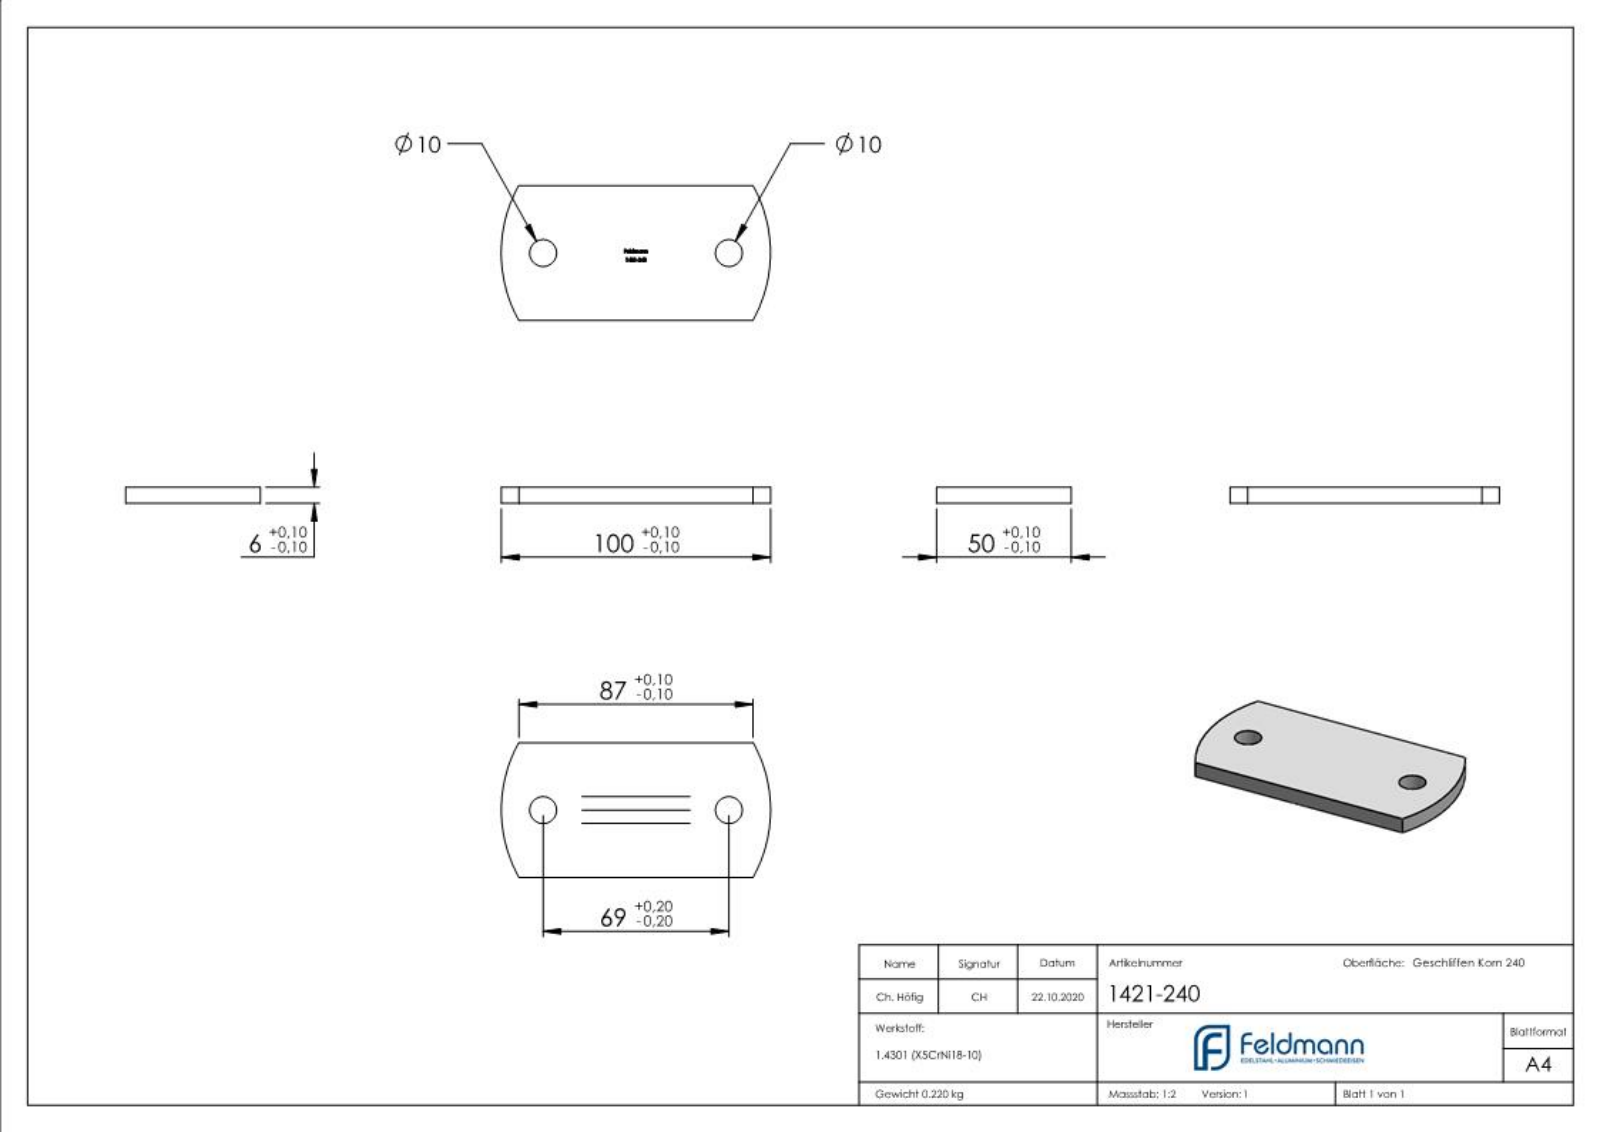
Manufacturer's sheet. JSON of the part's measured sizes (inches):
{"part_name": "1421-240", "step_written_by": "SolidWorks 2018 (CONFIG_CONTROL_DESIGN)", "units": "inches", "bodies": {"solids": 1, "faces": 209, "planar": 134, "cylindrical": 6, "other": 69}, "overall_size": [3.937, 1.969, 0.236], "volume_in3": 1.696, "surface_area_in2": 17.55, "round_holes": [[0.394, 2]], "partial_cylinders_radius": [[2.021, 2]], "face_to_face_distances": [0.236, 1.969, 0.232, 0.12, 0.108, 0.08, 0.071, 0.113, 0.984, 0.05], "hole_center_spacings": [2.717]}
